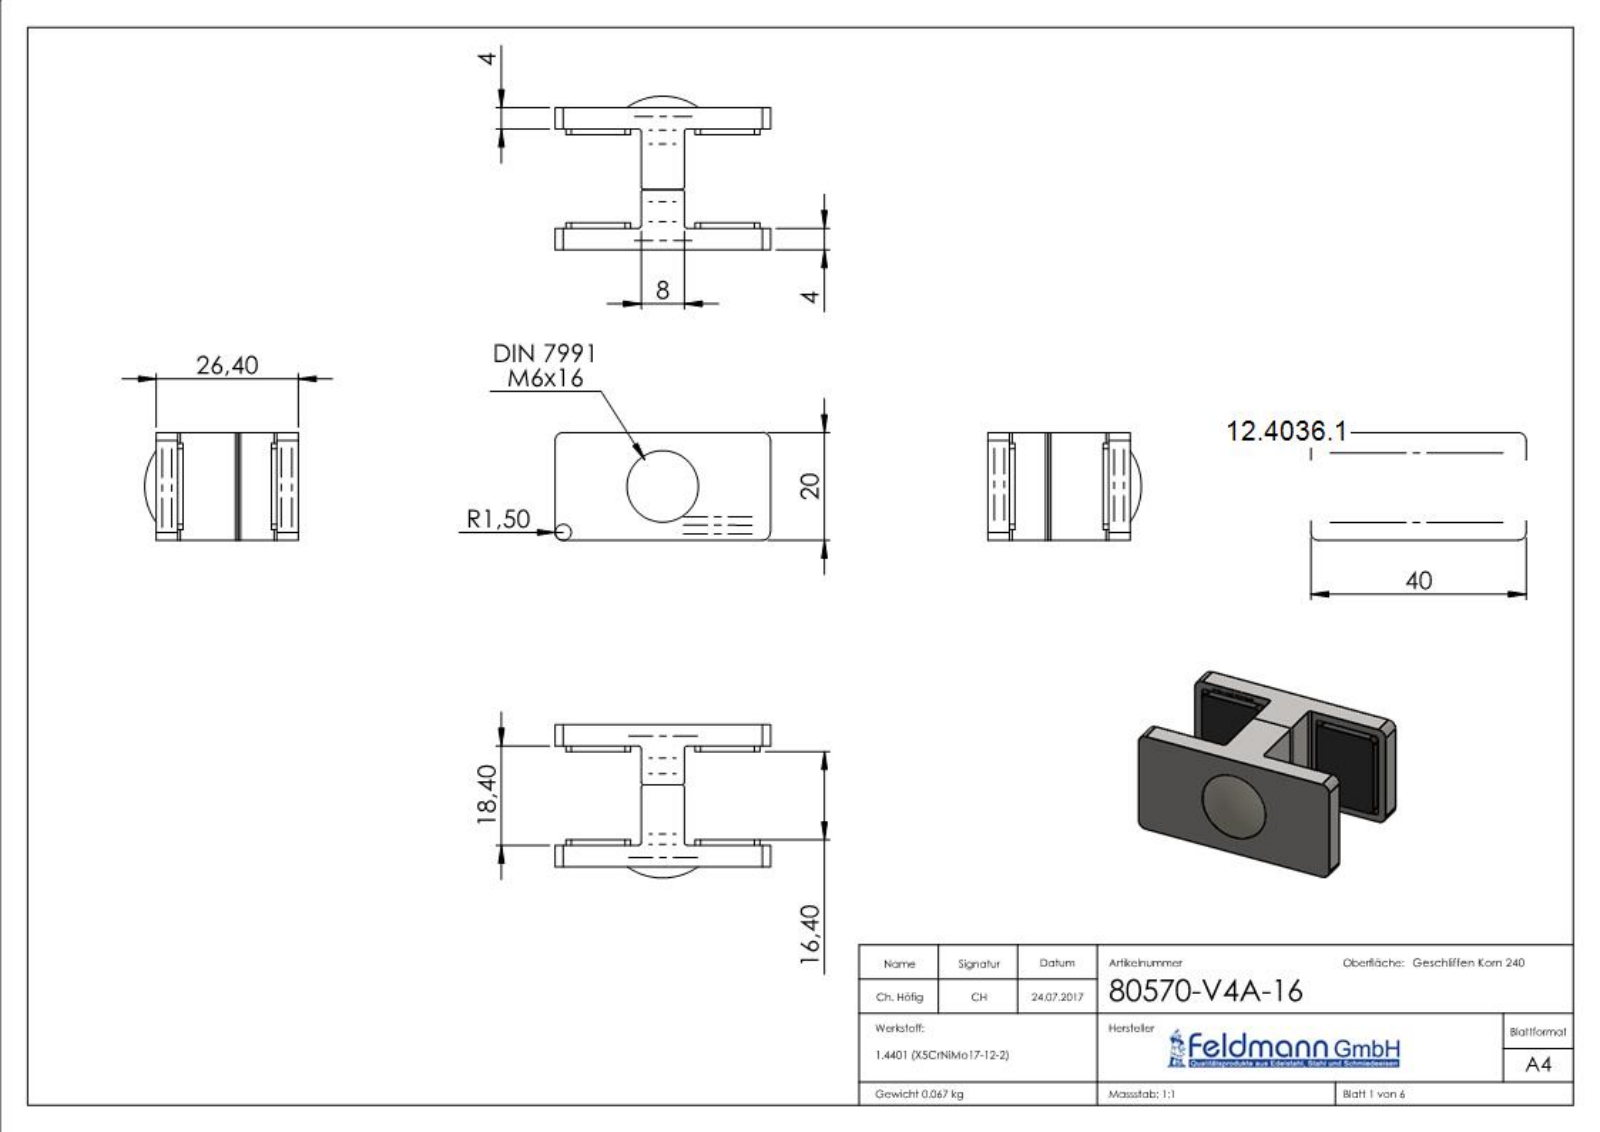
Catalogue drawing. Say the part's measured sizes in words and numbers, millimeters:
The part is named "80570-XXX-XX Teil1; 80570-XXX-XX Teil3_80570-240-XX Teil3; 80570-V4A-16; 80570-XXX-XX Teil1_80570-V4A-16 Teil1 (+7 more)". Its 3-D file was written by "SolidWorks 2018 (CONFIG_CONTROL_DESIGN)". It is 8 solids with 813 faces: 383 planar, 203 cylindrical and 227 other. Overall it measures 40 by 28.51 by 20 millimeters. Its volume is 9 641 cubic millimeters and its surface area 8 778 square millimeters. Round holes: 2 of diameter 2.7, 1 of diameter 1.8, 1 of diameter 5, 1 of diameter 6.5, 1 of diameter 12.5. Round bosses or shafts: 1 of diameter 12, 1 of diameter 6, 1 of diameter 4. Partial cylindrical surfaces (rounded edges, fillets, slot ends): 80 of radius 0.5, 12 of radius 0.2, 8 of radius 1, 4 of radius 0.19, 4 of radius 1.5. The main face-to-face distances are 3.5, 22.9, 1.5, 5, 26.4, 21.4, 17.9, 19.4, 2, 0.5. The hole center spacings are 6.5, 13.
